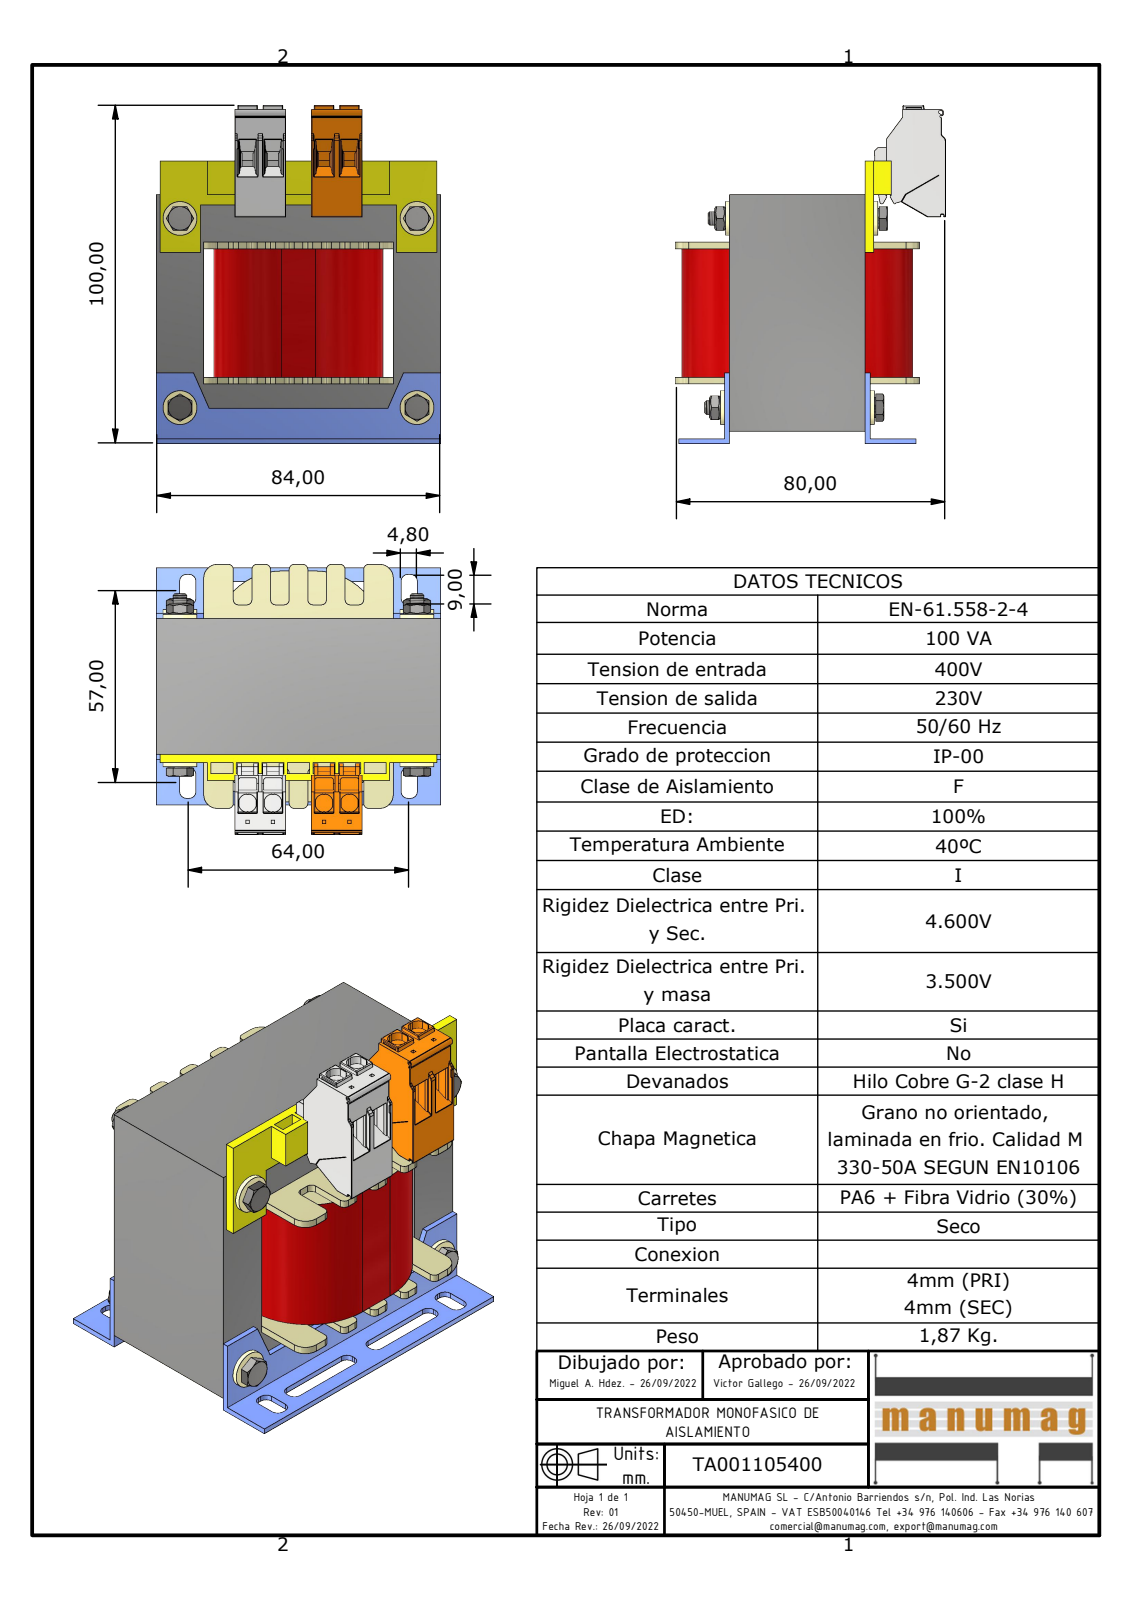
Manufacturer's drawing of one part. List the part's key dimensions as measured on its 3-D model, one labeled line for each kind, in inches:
Part name (STEP PRODUCT): TA001105400; EI84 x 70 - 40 (RC28); EI84; AF28DIN (+6 more)
STEP written by: Autodesk Inventor 2023 (AUTOMOTIVE_DESIGN)
Units: inches
Bodies: 23 solids, 3793 faces (3023 planar, 528 cylindrical, 242 other)
Overall size (bounding box): 3.945 × 3.307 × 3.138
Volume: 17.86 in³ · Surface area: 134.1 in²
Round holes (diameter × count): ⌀0.128 ×4, ⌀0.157 ×4, ⌀0.177 ×4
Round bosses / shafts (diameter × count): ⌀0.394 ×4, ⌀0.232 ×4, ⌀0.193 ×4, ⌀0.143 ×4
Partial cylindrical surfaces — rounded edges, fillets, slot ends (radius × count): R0.006 ×160, R0.008 ×48, R0.079 ×40, R0.059 ×32, R0.02 ×12, R0.012 ×7, R0.039 ×4, R0.106 ×4
Main face-to-face distances: 0.551, 2.205, 1.575, 1.102, 1.654, 2.756, 0.059, 0.079, 2.126, 3.307
Hole centre spacings: 2.205, 2.756, 3.529
